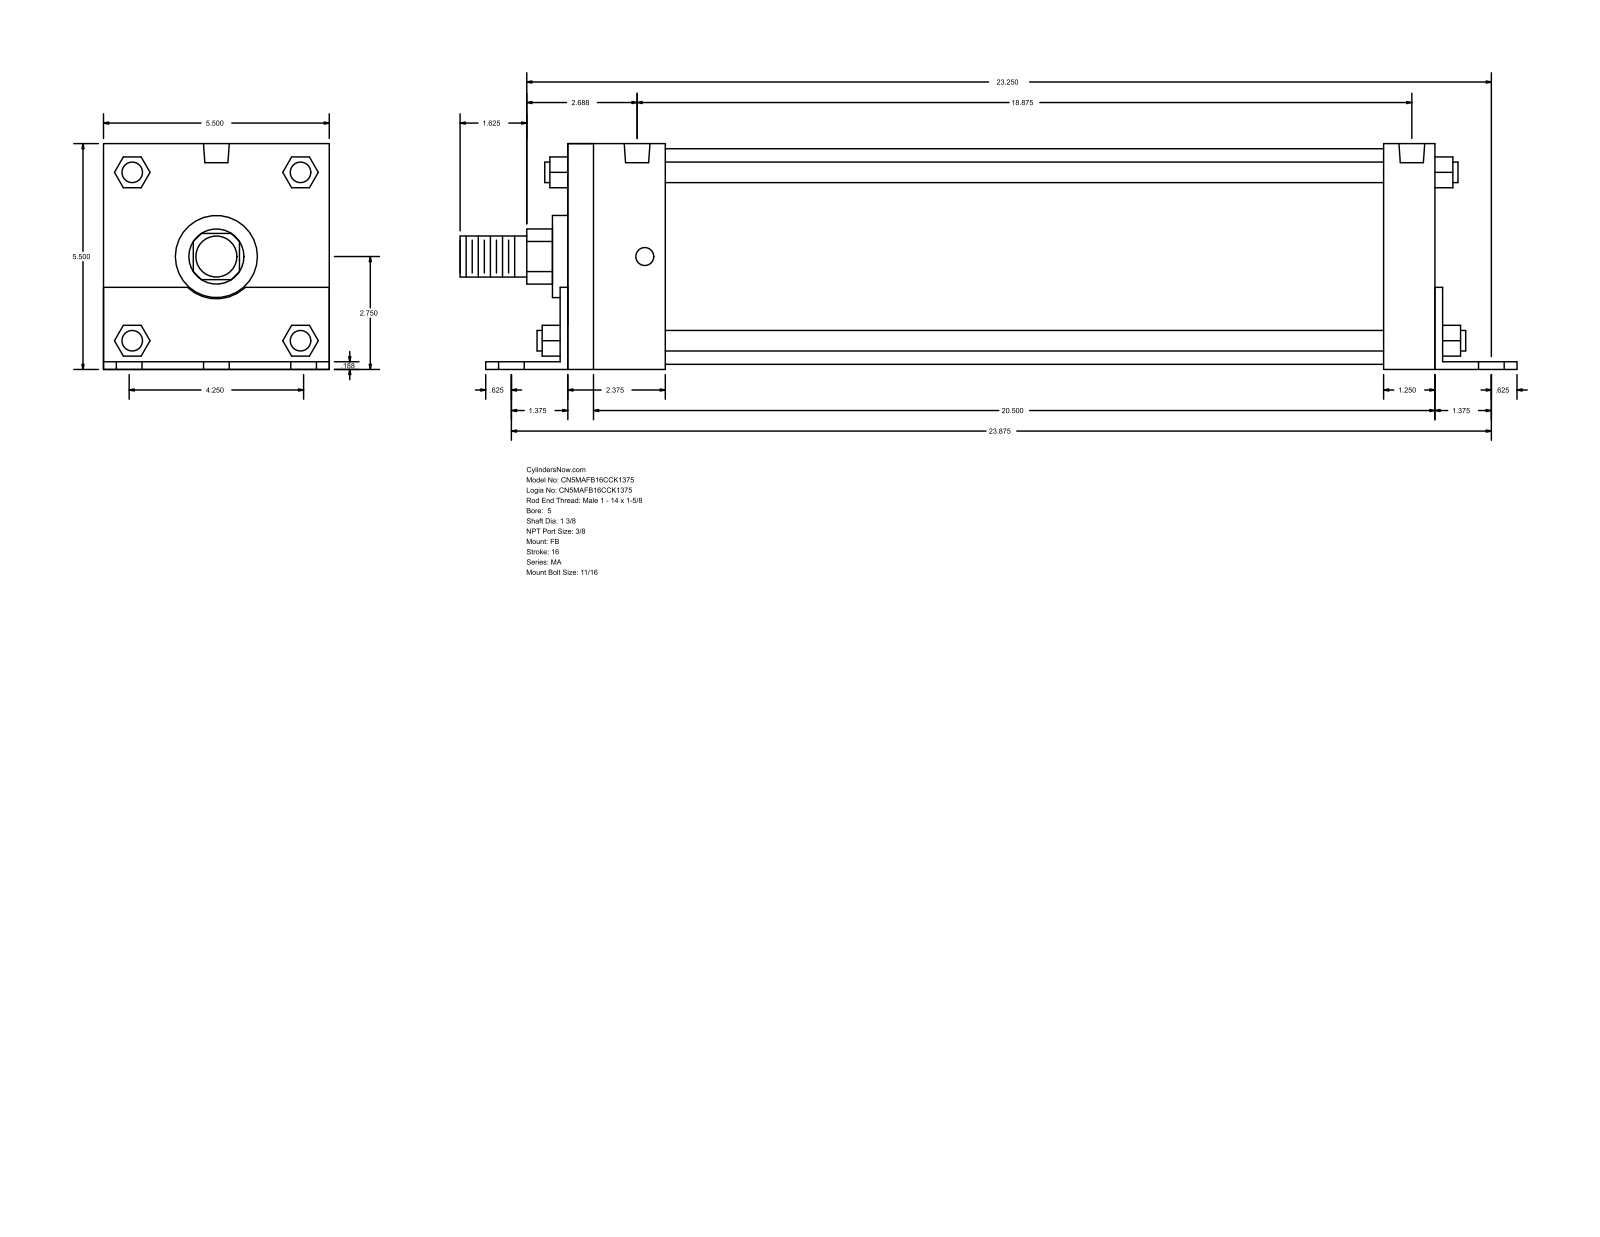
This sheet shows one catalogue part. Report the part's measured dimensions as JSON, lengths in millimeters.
{"part_name": "MA_FB__0500_1.375", "step_written_by": "GSSL Pune (CONFIG_CONTROL_DESIGN)", "units": "millimeters", "bodies": {"solids": 0, "faces": 140, "planar": 105, "cylindrical": 35, "other": 0}, "overall_size": [654.05, 139.75, 139.7], "round_holes": [[17.46, 6], [11.11, 4], [15.93, 2]], "round_bosses_or_shafts": [[12.7, 4], [133.35, 1], [50.8, 1], [34.92, 1], [25.4, 1]], "partial_cylinders_radius": [[17.06, 1], [26.16, 1]], "face_to_face_distances": [139.7, 4.76, 139.75, 541.34, 4.71, 134.99, 536.58, 546.1, 31.75, 36.51], "hole_center_spacings": [53.98, 608.83, 606.43, 4.77, 73.04, 76.34, 94.68, 98.64]}
